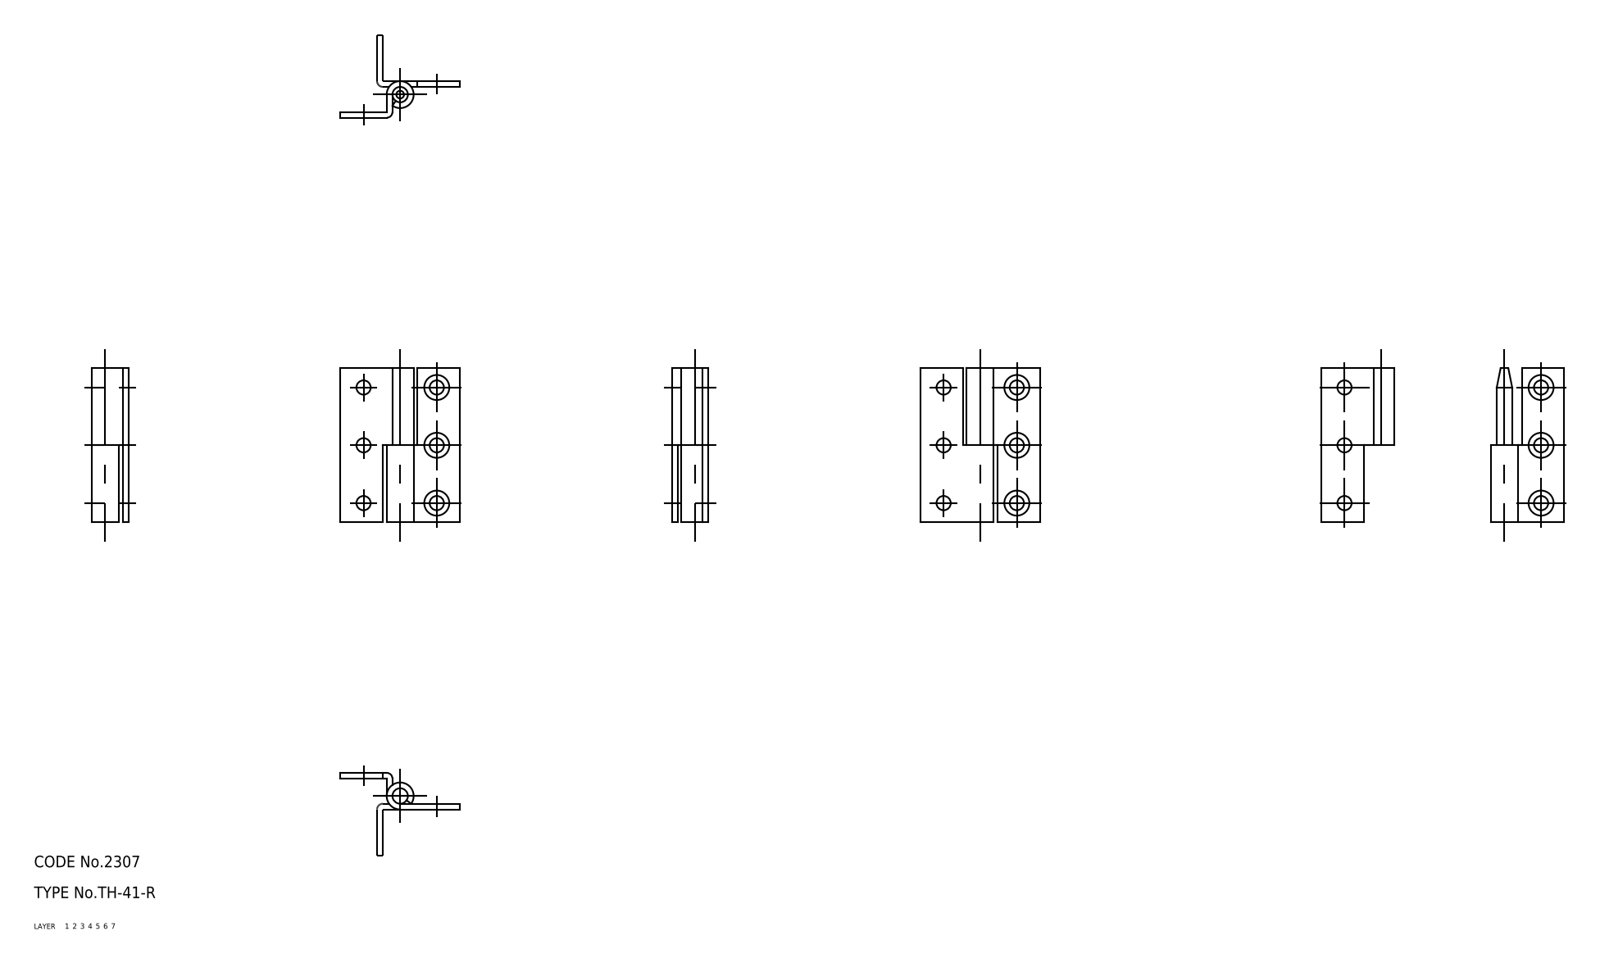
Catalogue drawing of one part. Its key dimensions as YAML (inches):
part_name: "shaft; hinge piece_B; hinge piece_A; TH_41_R_8931_36"
step_written_by: "CADfix (AUTOMOTIVE_DESIGN)"
units: inches
bodies: {solids: 3, faces: 53, planar: 0, cylindrical: 0, other: 53}
overall_size: [1.575, 1.22, 0.374]
volume: 0.172
surface_area: 6.569
